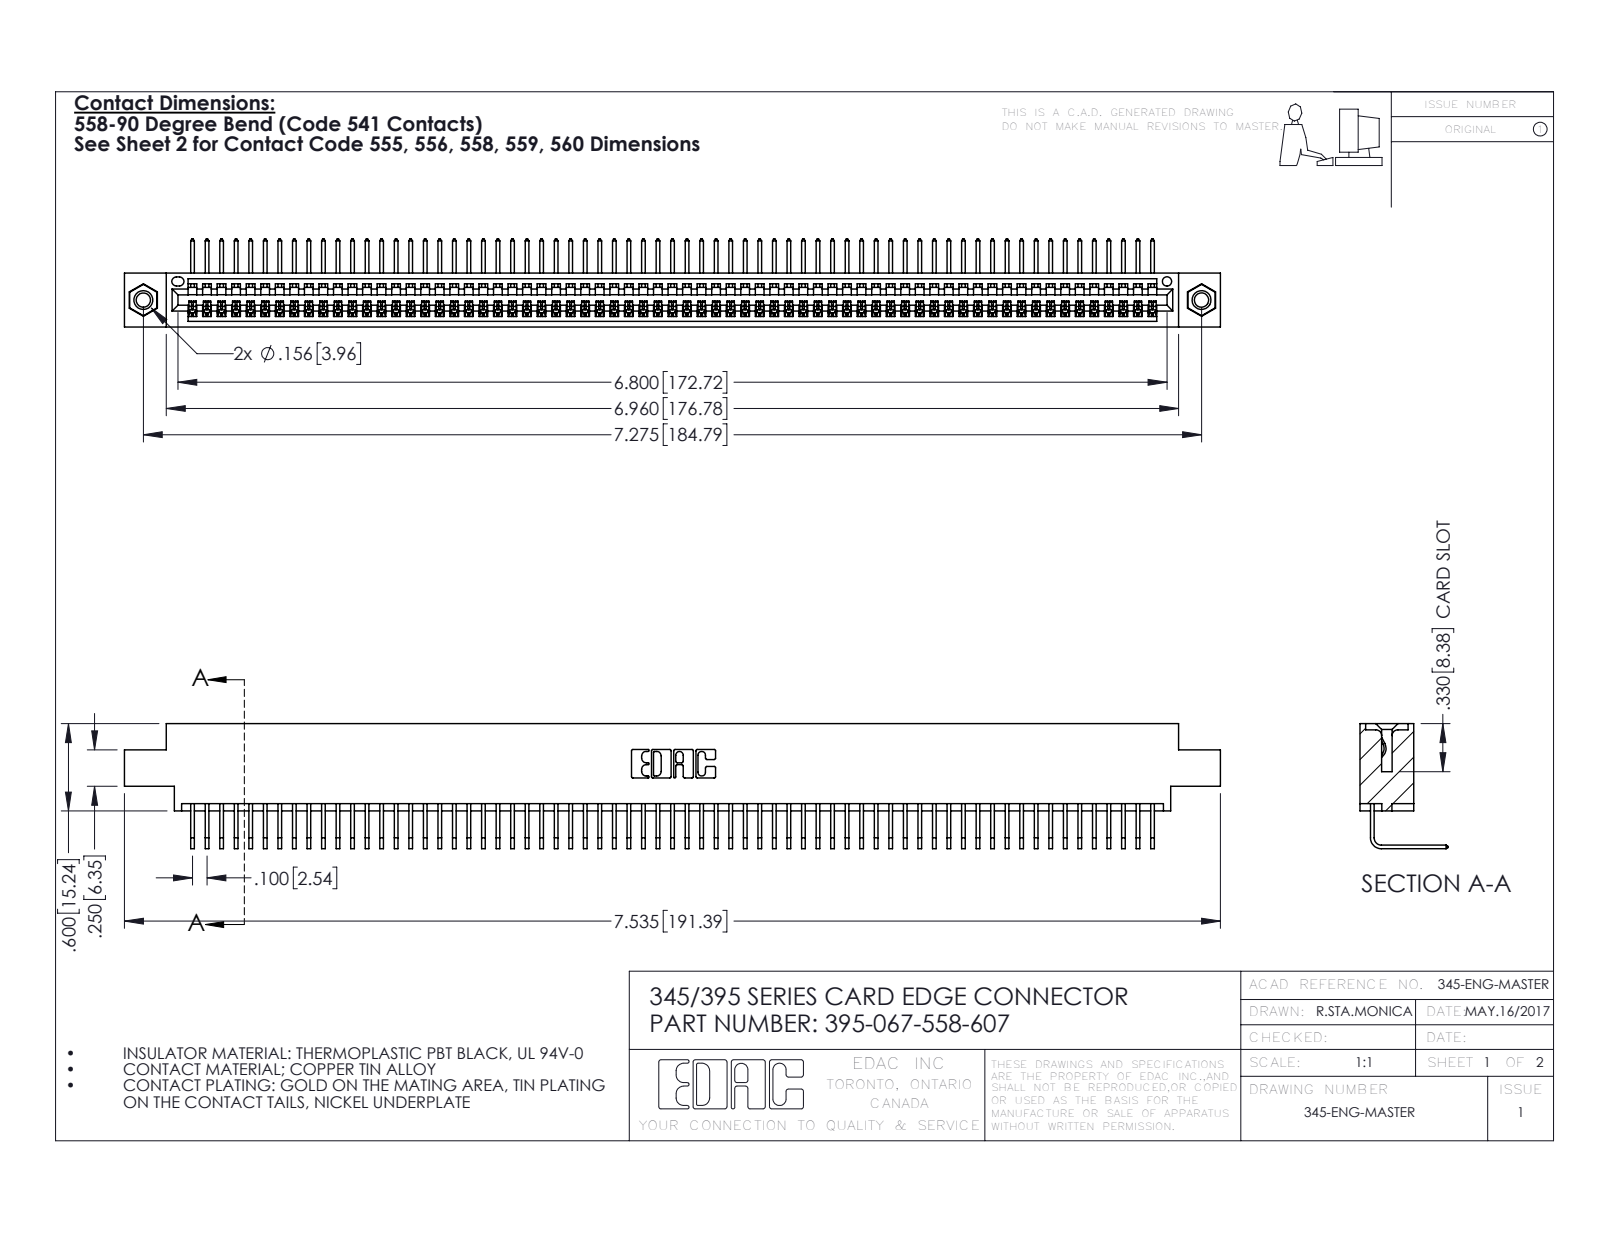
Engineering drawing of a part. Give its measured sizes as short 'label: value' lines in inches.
name: 345-292-001_558 Tail - 2; 345 Part_0.170 Offset - 0.156 Dia-TI; 345-250-001_345-250-005-103; 395-067-558-607
written by: SolidWorks 2016 (CONFIG_CONTROL_DESIGN)
unit: in
bodies: 70 solids, 4210 faces (2930 planar, 1264 cylindrical, 16 other)
size: 7.535 × 0.859 × 0.605
volume: 1.128 in³; area: 40.87 in²
holes: 2× ⌀0.098, 2× ⌀0.125, 2× ⌀0.156, 1× ⌀0.064
bosses: 2× ⌀0.155
rounds: 134× R0.006, 22× R0.01, 6× R0.007, 6× R0.031, 3× R0.026, 2× R0.031, 2× R0.04, 1× R0.014
face distances: 0.072, 0.298, 0.37, 0.2, 0.098, 0.272, 0.025, 0.225, 0.175, 0.149
hole spacings: 0.27, 7.039, 7.275
